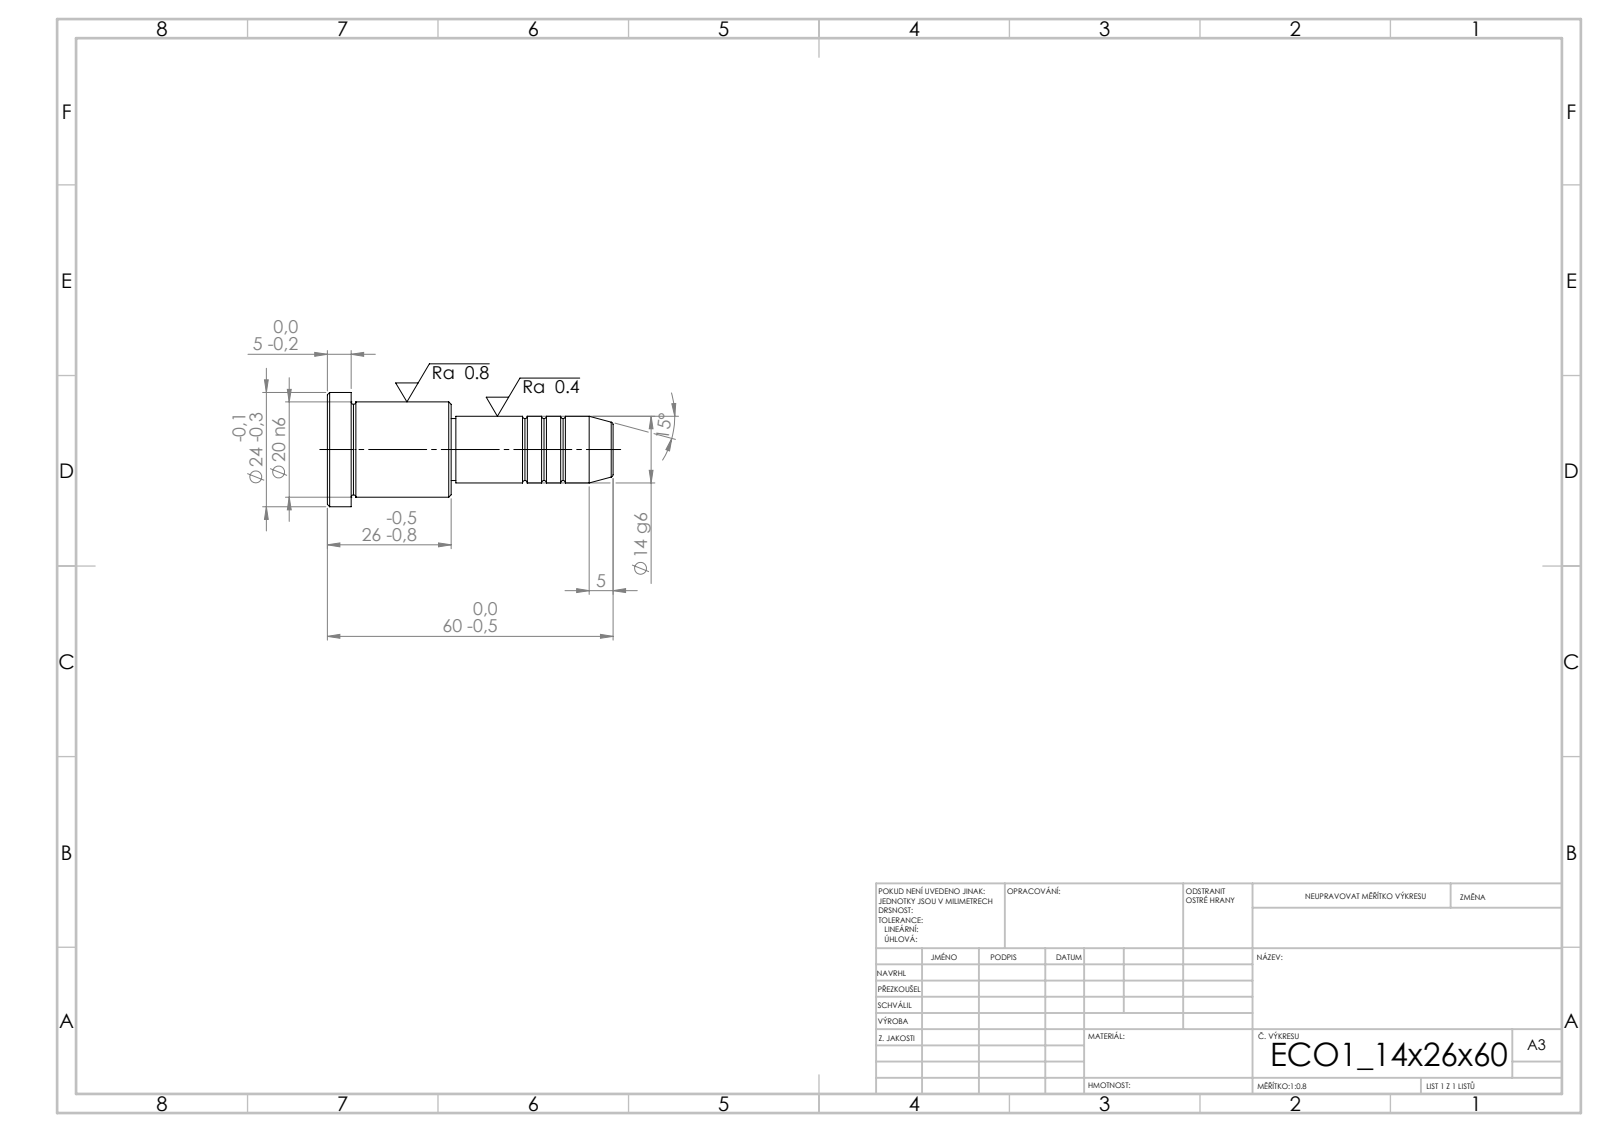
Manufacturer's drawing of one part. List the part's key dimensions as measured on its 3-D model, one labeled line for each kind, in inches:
STEP written by: SolidWorks 2019 (CONFIG_CONTROL_DESIGN)
Units: inches
Bodies: 1 solid, 43 faces (5 planar, 14 cylindrical, 24 other)
Overall size (bounding box): 2.362 × 0.945 × 0.945
Volume: 0.845 in³ · Surface area: 6.389 in²
Round bosses / shafts (diameter × count): ⌀0.945 ×1, ⌀0.787 ×1, ⌀0.551 ×1, ⌀0.512 ×1
Main face-to-face distances: 1.024, 0.827, 0.197, 1.339, 2.165, 2.362, 1.299, 0.039, 0.866, 1.063
